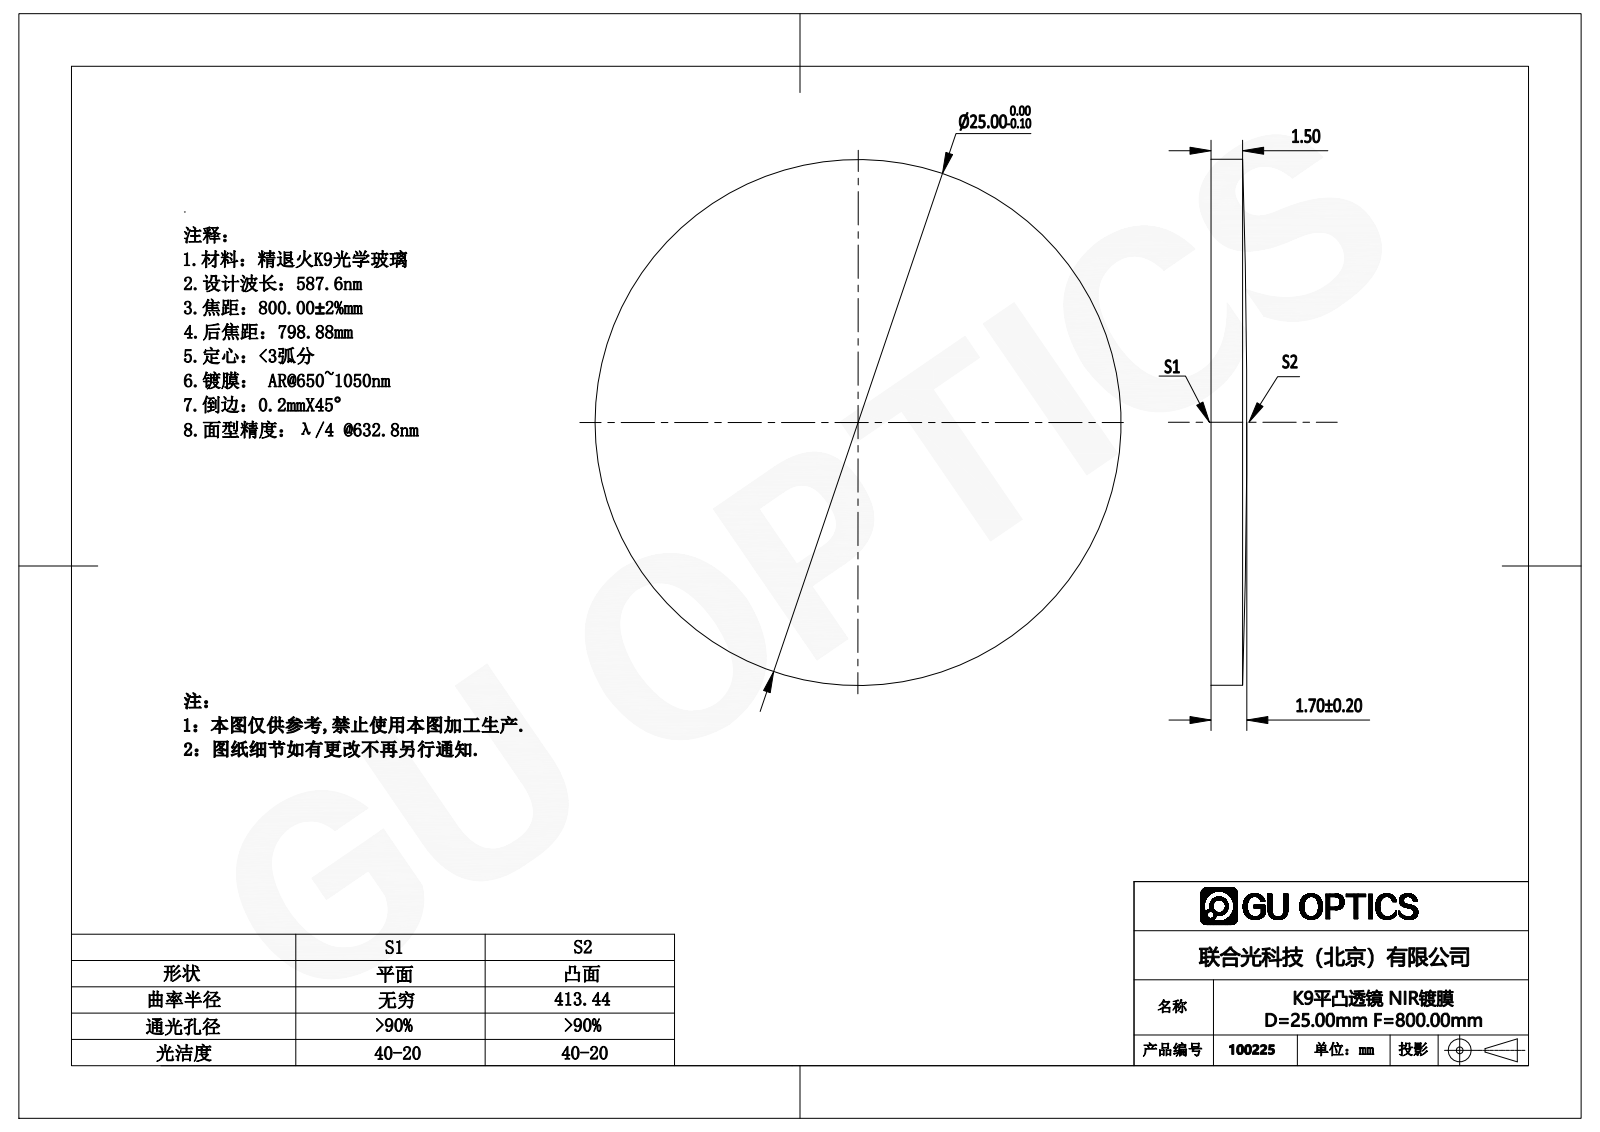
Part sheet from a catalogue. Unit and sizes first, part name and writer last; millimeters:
Units: millimetres
Overall size (bounding box): 25 × 25 × 1.7
Round bosses / shafts (diameter × count): ⌀25 ×1
Volume: 785 mm³ · Surface area: 1 100 mm²
Bodies: 1 solid, 5 faces (1 planar, 2 cylindrical, 2 other)
Part name (STEP PRODUCT): 100225
STEP written by: SolidWorks 2016 (AUTOMOTIVE_DESIGN)
